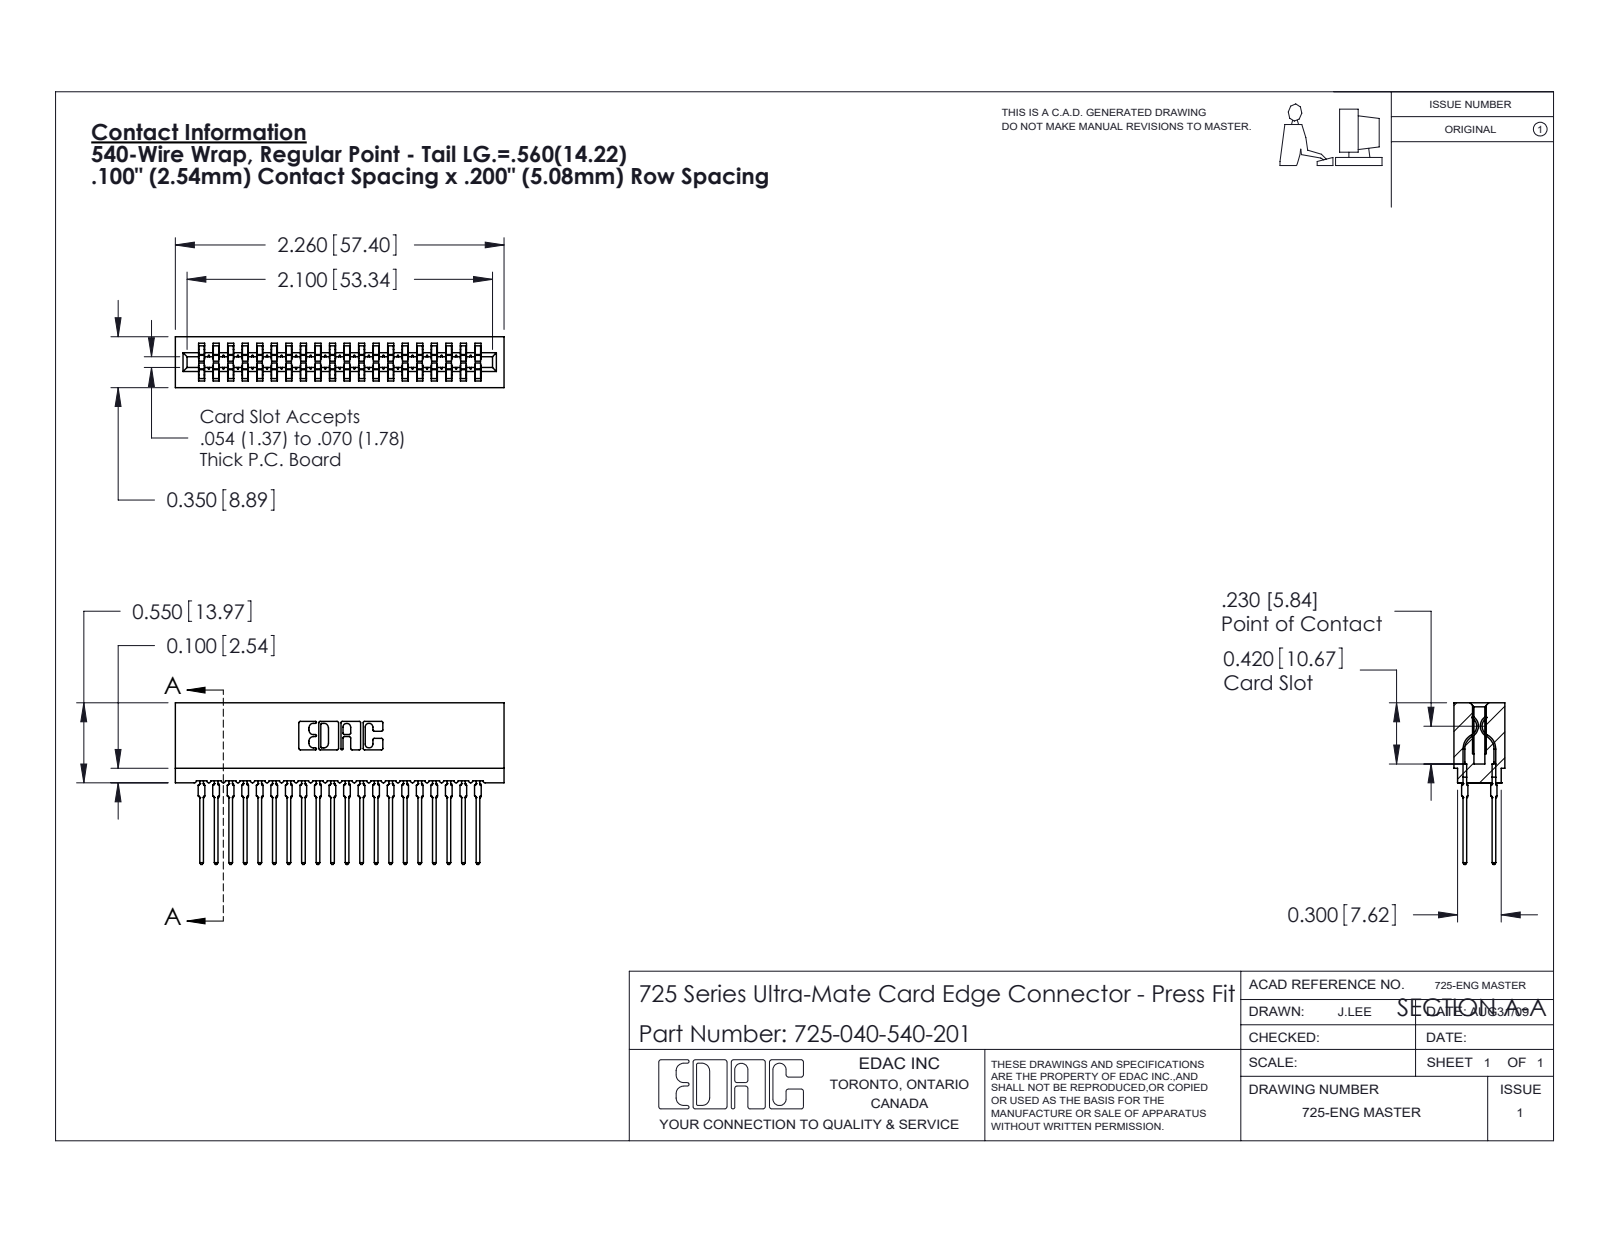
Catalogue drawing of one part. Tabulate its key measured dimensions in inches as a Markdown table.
| quantity | value |
| --- | --- |
| part name | 725 Part_Insulator Option - 01; 745-292-001_540; 725-040-540-201 |
| STEP written by | SolidWorks 2020 (CONFIG_CONTROL_DESIGN) |
| units | inches |
| bodies | 41 solids, 3675 faces (1895 planar, 740 cylindrical, 1040 other) |
| overall size | 2.26 × 1.111 × 0.35 |
| volume | 0.292 in³ |
| surface area | 15.64 in² |
| partial cylindrical surfaces (radius × count) | 0.021 × 80, 0.015 × 40, 0.01 × 22, 0.005 × 8, 0.011 × 8, 0.007 × 6, 0.031 × 6, 0.026 × 3 |
| main face-to-face distances | 0.2, 0.1, 0.4, 0.3, 0.063, 0.287, 0.5, 0.6, 0.7, 0.35 |
